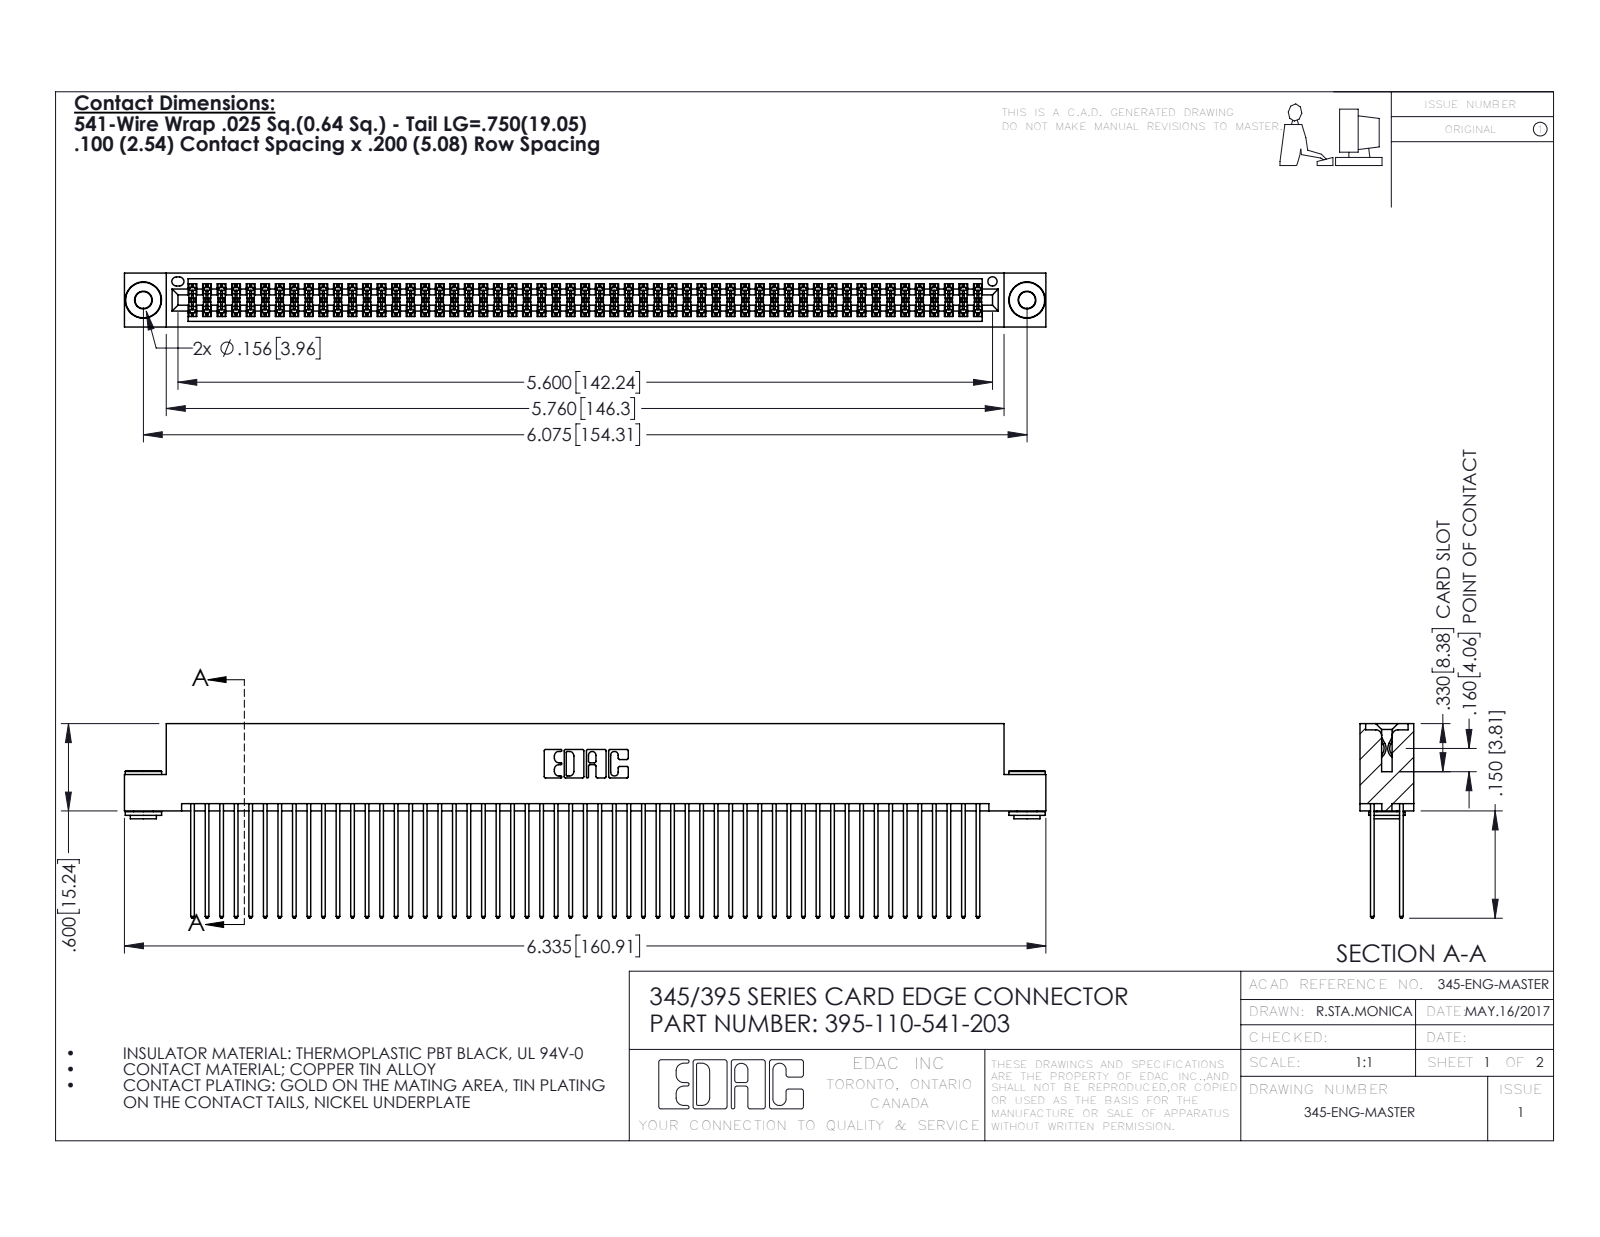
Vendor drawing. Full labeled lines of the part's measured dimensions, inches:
Part name (STEP PRODUCT): 345-292-001_345-293-141; 395-110-541-203; 345 Part_Flush Mounting Lugs - 0.156 Dia-TH; 345-250-002_345-250-002-102
STEP written by: SolidWorks 2016 (CONFIG_CONTROL_DESIGN)
Units: inches
Bodies: 113 solids, 5664 faces (3720 planar, 1936 cylindrical, 8 other)
Overall size (bounding box): 6.335 × 1.337 × 0.37
Volume: 1.001 in³ · Surface area: 42.89 in²
Round holes (diameter × count): ⌀0.116 ×2, ⌀0.156 ×2, ⌀0.064 ×1
Round bosses / shafts (diameter × count): ⌀0.25 ×2, ⌀0.18 ×2, ⌀0.136 ×2
Partial cylindrical surfaces — rounded edges, fillets, slot ends (radius × count): R0.006 ×165, R0.01 ×110, R0.01 ×22, R0.007 ×6, R0.031 ×6, R0.026 ×3, R0.014 ×2, R0.019 ×2
Main face-to-face distances: 0.072, 0.298, 0.2, 0.025, 0.098, 0.272, 0.225, 0.37, 0.175, 0.149
Hole centre spacings: 0.27, 5.839, 6.075
